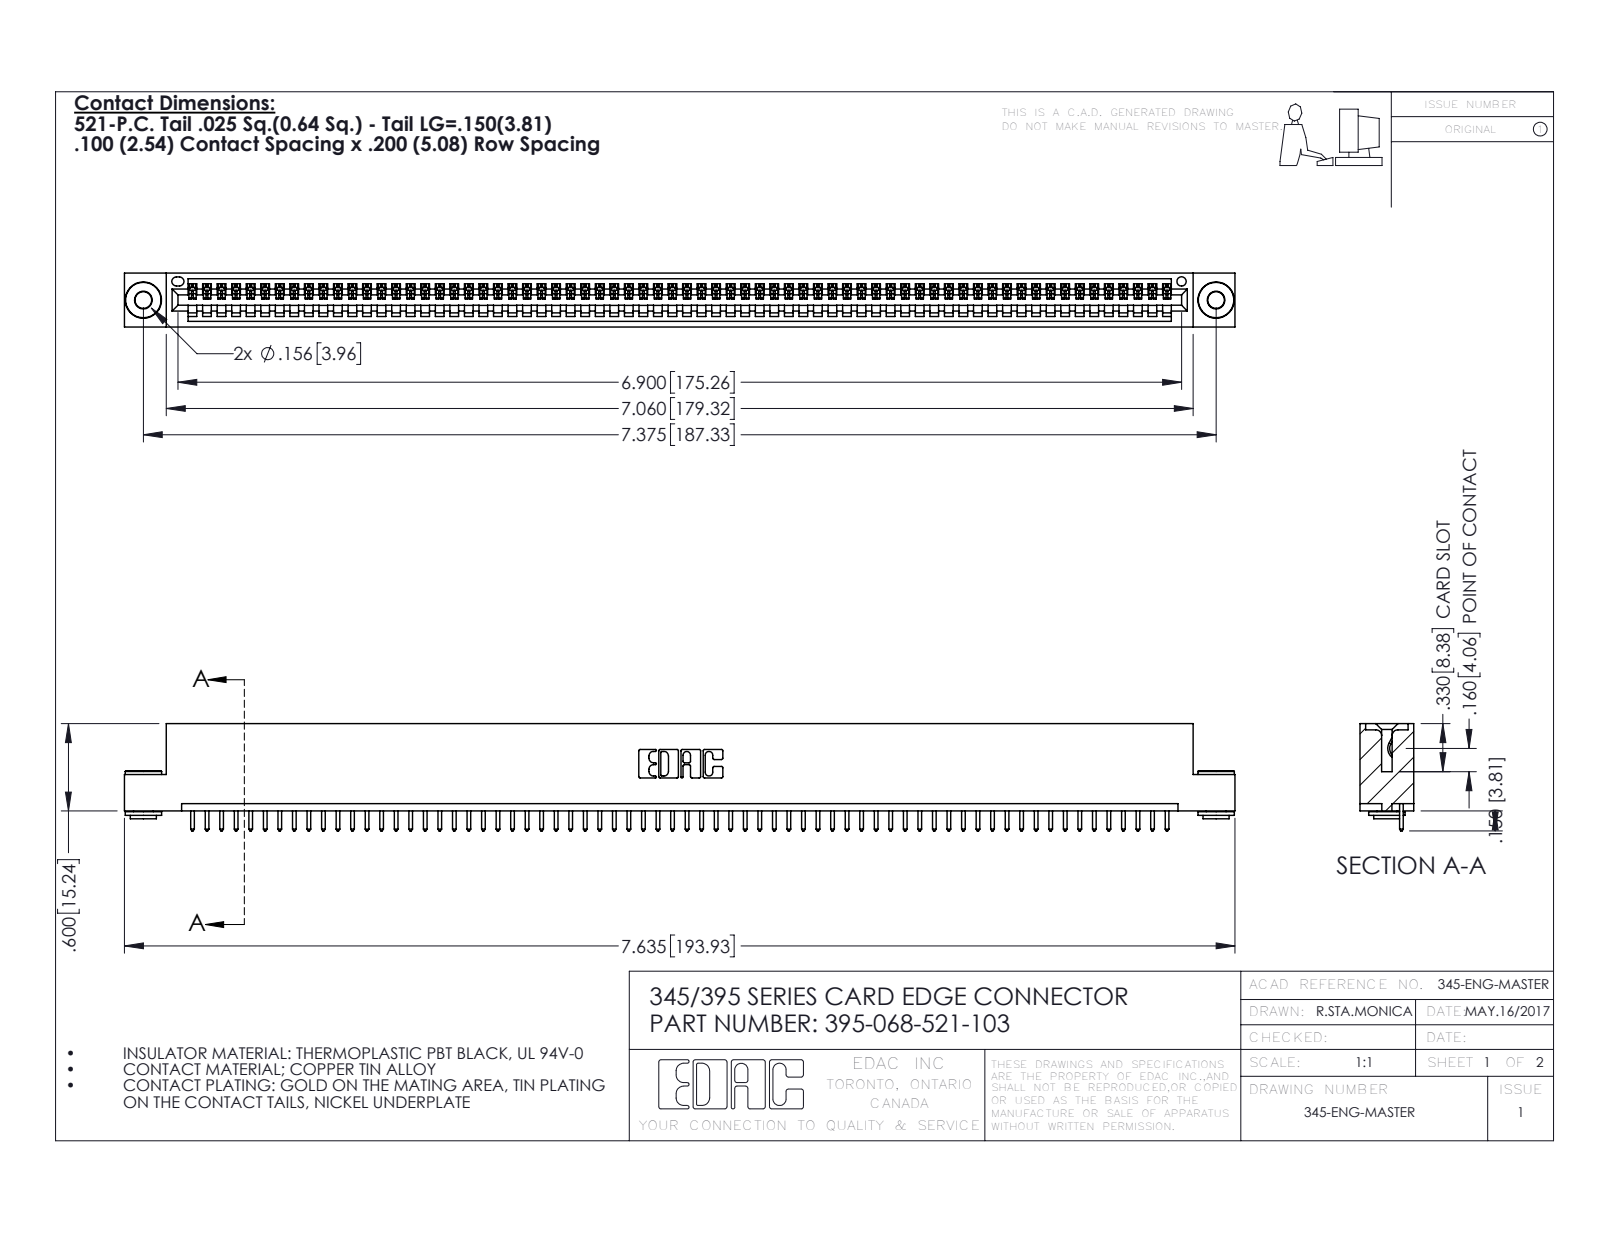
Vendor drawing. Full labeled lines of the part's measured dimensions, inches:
Part name (STEP PRODUCT): 345-250-002_345-250-002-102; 395-068-521-103; 345-292-001_345-293-121; 345 Part_Flush Mounting Lugs - 0.156 Dia-TH
STEP written by: SolidWorks 2016 (CONFIG_CONTROL_DESIGN)
Units: inches
Bodies: 71 solids, 4108 faces (2810 planar, 1290 cylindrical, 8 other)
Overall size (bounding box): 7.635 × 0.737 × 0.37
Volume: 1.126 in³ · Surface area: 37.73 in²
Round holes (diameter × count): ⌀0.116 ×2, ⌀0.156 ×2, ⌀0.064 ×1
Round bosses / shafts (diameter × count): ⌀0.25 ×2, ⌀0.18 ×2, ⌀0.136 ×2
Partial cylindrical surfaces — rounded edges, fillets, slot ends (radius × count): R0.006 ×136, R0.01 ×136, R0.01 ×22, R0.007 ×6, R0.031 ×6, R0.026 ×3, R0.031 ×2, R0.04 ×2
Main face-to-face distances: 0.072, 0.298, 0.37, 0.2, 0.025, 0.098, 0.272, 0.225, 0.149, 0.072
Hole centre spacings: 0.27, 7.139, 7.375
